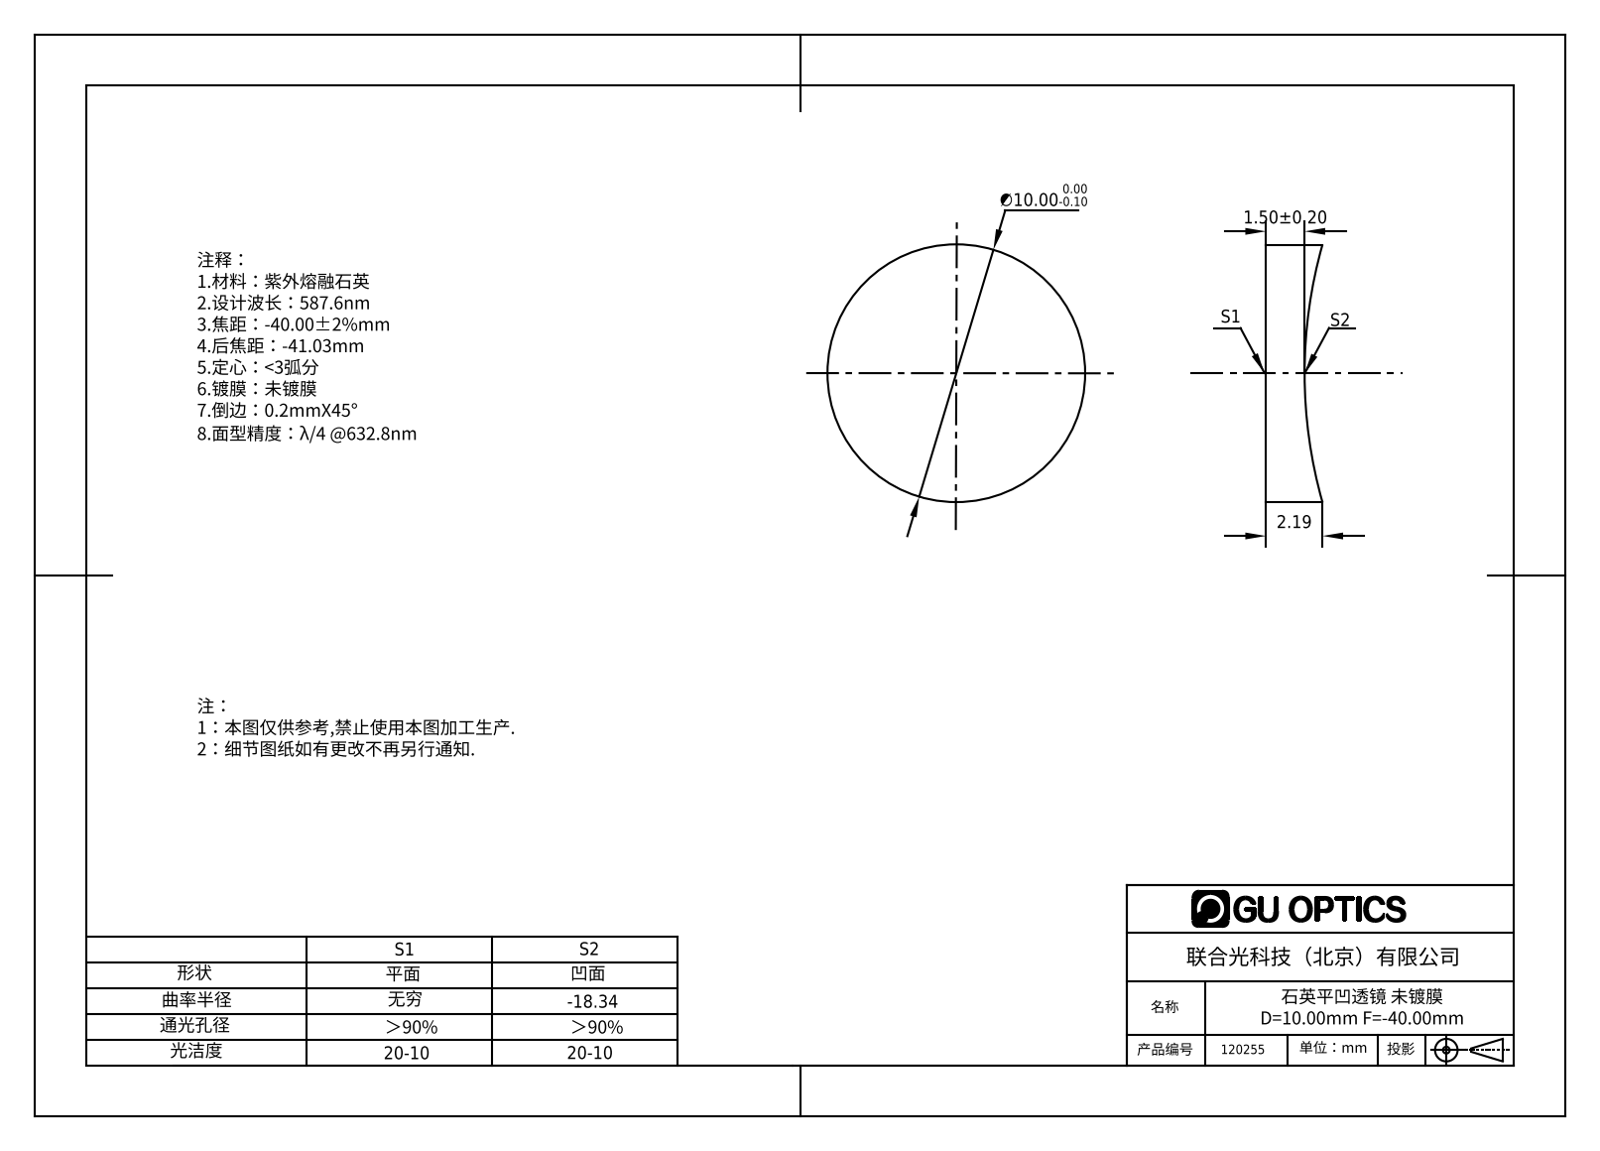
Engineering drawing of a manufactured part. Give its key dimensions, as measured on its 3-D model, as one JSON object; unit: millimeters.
{"part_name": "120255", "step_written_by": "SolidWorks 2016 (AUTOMOTIVE_DESIGN)", "units": "millimeters", "bodies": {"solids": 1, "faces": 5, "planar": 1, "cylindrical": 2, "other": 2}, "overall_size": [10, 10, 2.19], "volume_mm3": 145, "surface_area_mm2": 228, "round_bosses_or_shafts": [[10, 1]]}
